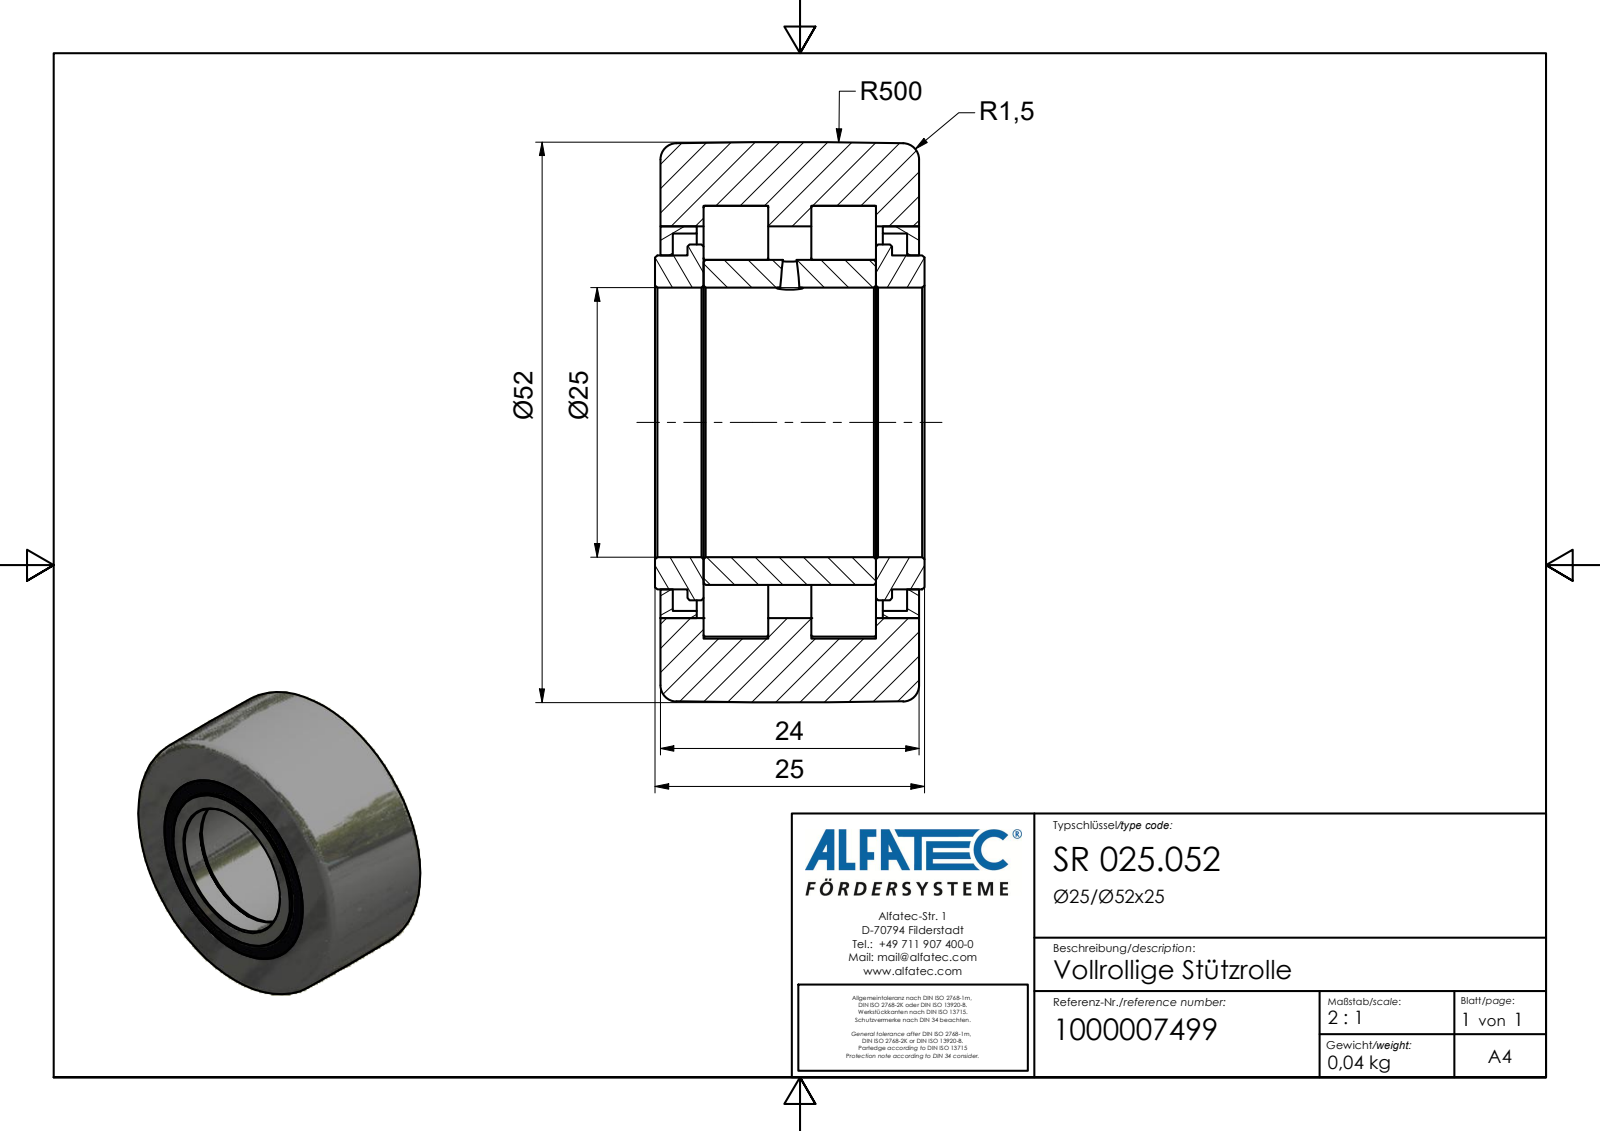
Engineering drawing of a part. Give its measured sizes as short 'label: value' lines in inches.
name: SR 025.052_Kontur
written by: Autodesk Inventor 2020 (AUTOMOTIVE_DESIGN)
unit: in
bodies: 1 solid, 246 faces (80 planar, 85 cylindrical, 81 other)
size: 2.047 × 2.047 × 0.984
volume: 2.071 in³; area: 29.3 in²
holes: 1× ⌀0.098, 1× ⌀0.984, 1× ⌀1.378, 1× ⌀1.431, 1× ⌀1.581
bosses: 16× ⌀0.197, 1× ⌀1.299, 1× ⌀1.22, 1× ⌀1.188
face distances: 0.394, 0.945, 0.157, 0.787, 0.551, 0.236, 0.02, 0.177, 0.413, 0.571
